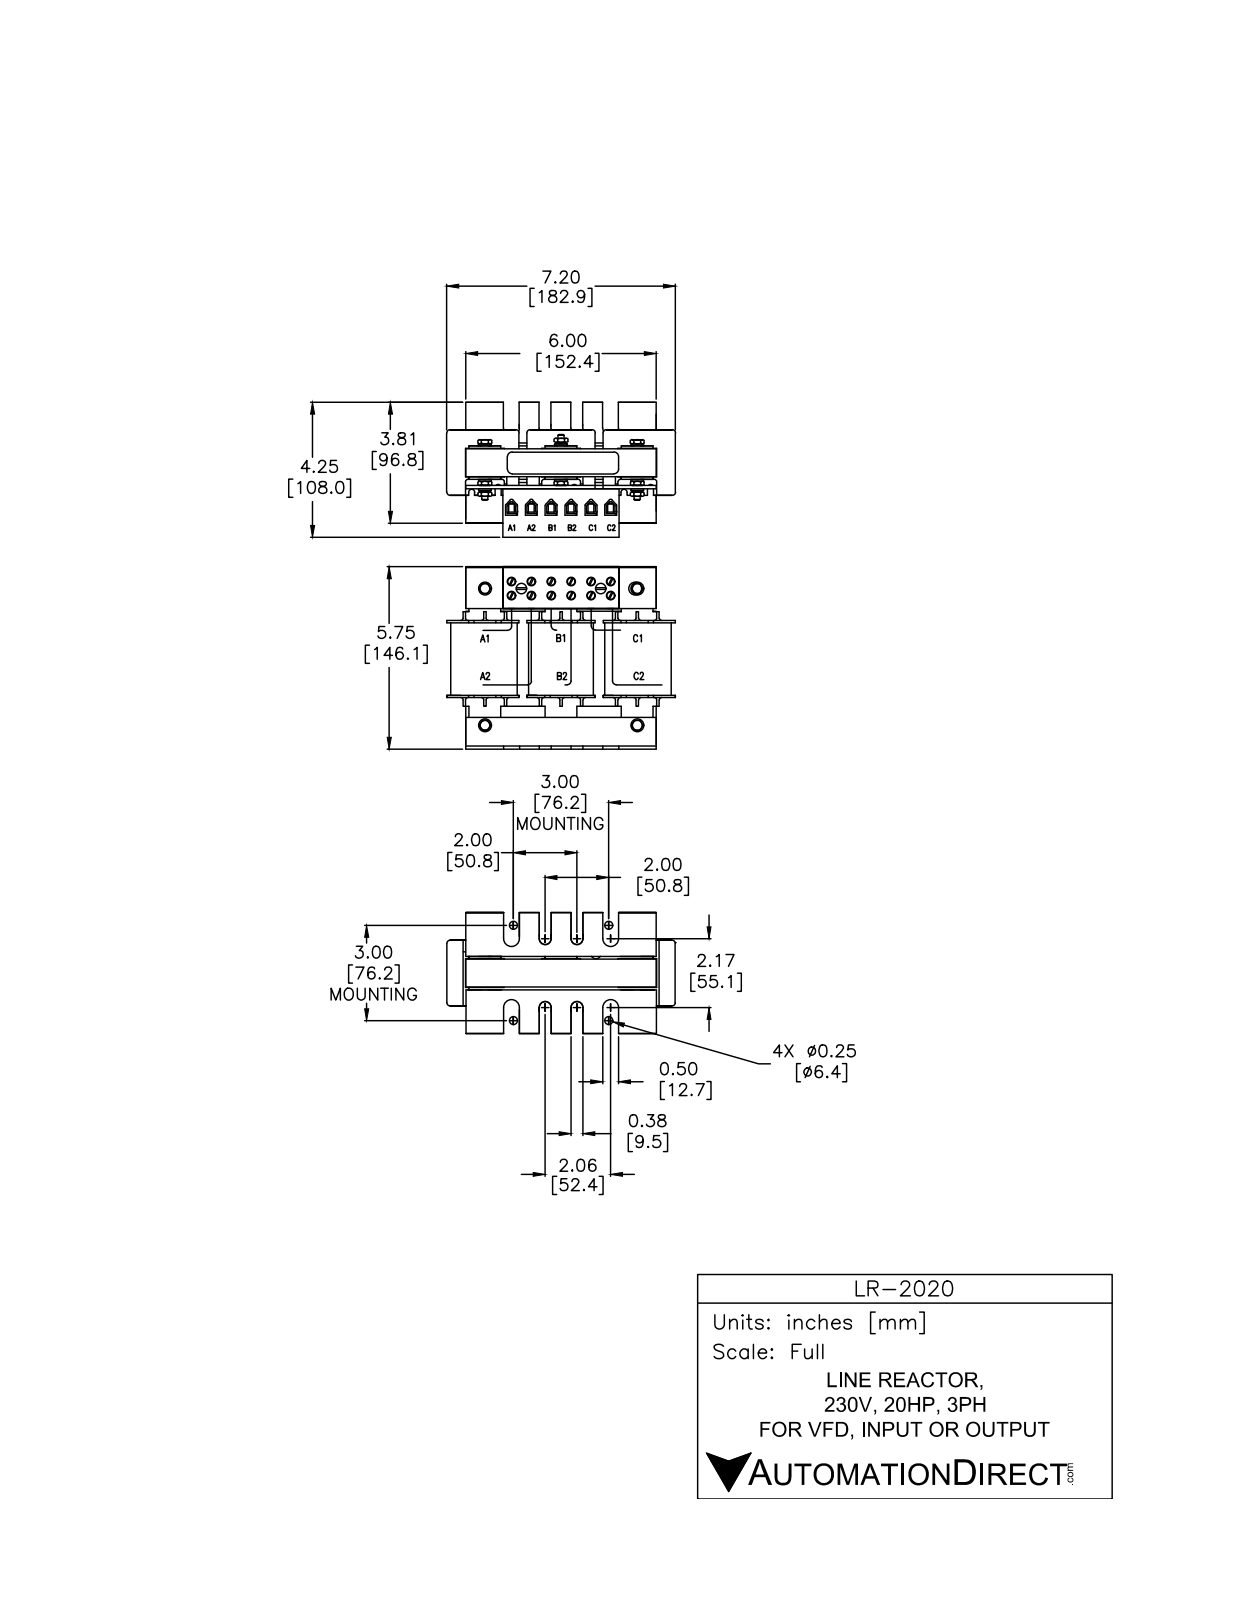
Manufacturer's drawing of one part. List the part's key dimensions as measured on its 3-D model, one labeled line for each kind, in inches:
Part name (STEP PRODUCT): LR-2020
STEP written by: SolidWorks 2011 (AUTOMOTIVE_DESIGN)
Units: inches
Bodies: 34 solids, 1041 faces (767 planar, 242 cylindrical, 32 other)
Overall size (bounding box): 7.008 × 5.619 × 3.907
Volume: 51.71 in³ · Surface area: 302.9 in²
Round holes (diameter × count): ⌀0.276 ×12, ⌀0.305 ×5
Round bosses / shafts (diameter × count): ⌀0.472 ×5, ⌀0.413 ×5, ⌀0.305 ×2, ⌀0.183 ×2, ⌀0.184 ×1, ⌀0.183 ×1, ⌀0.183 ×1
Partial cylindrical surfaces — rounded edges, fillets, slot ends (radius × count): R0.106 ×24, R0.197 ×12, R0.276 ×12, R0.089 ×6, R0.059 ×4, R0.177 ×4, R0.246 ×4, R0.128 ×2
Main face-to-face distances: 0.079, 0.364, 2.441, 1.329, 1.407, 0.108, 0.344, 0.266, 0.443, 0.187
Hole centre spacings: 0.63, 1.26, 0.376, 0.394, 0.77, 0.96, 0.981, 1.335
